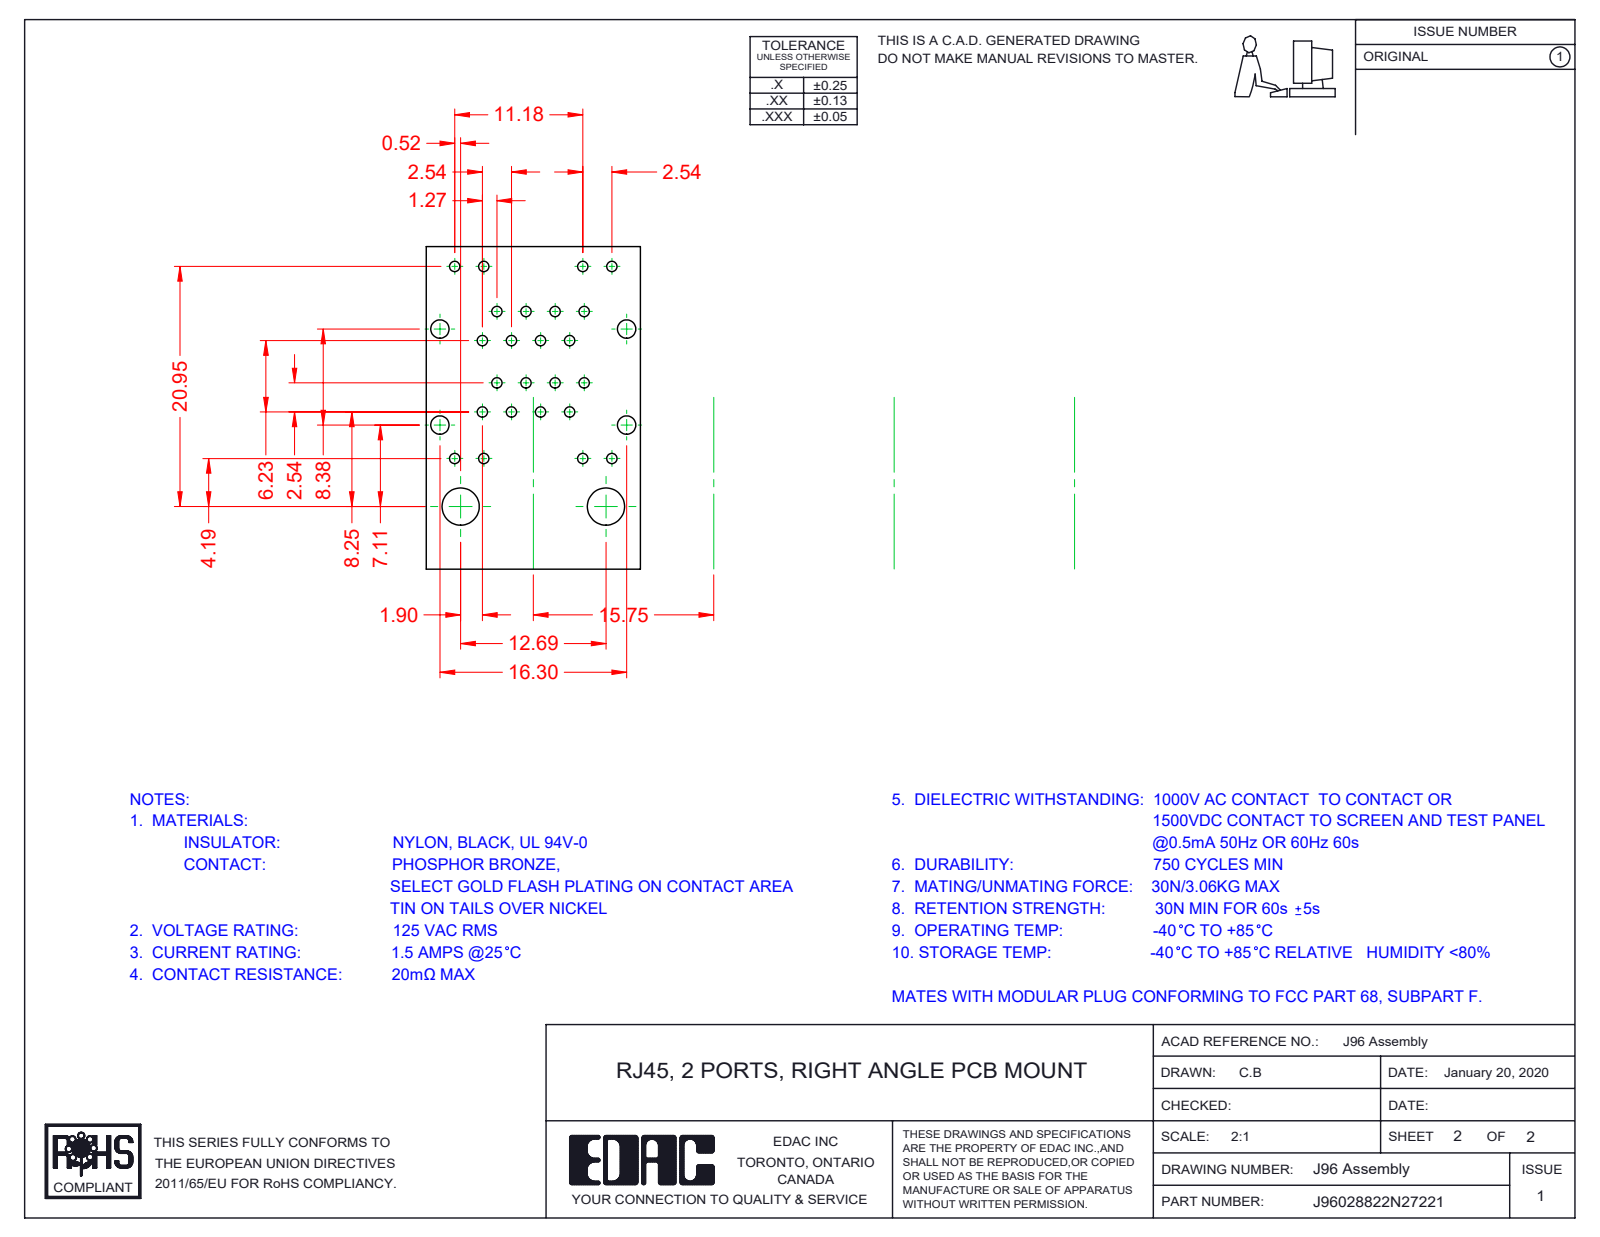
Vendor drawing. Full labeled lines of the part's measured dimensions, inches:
Part name (STEP PRODUCT): 96 LED LH Upper_2-Red; 96 Insulator Insert; 96 LED RH Upper_7-Green-Orange; 96 Contact Lock Upper (+8 more)
STEP written by: SolidWorks 2016 (CONFIG_CONTROL_DESIGN)
Units: inches
Bodies: 27 solids, 2421 faces (1865 planar, 450 cylindrical, 106 other)
Overall size (bounding box): 1.235 × 1.129 × 0.661
Volume: 0.418 in³ · Surface area: 29.6 in²
Partial cylindrical surfaces — rounded edges, fillets, slot ends (radius × count): R0.01 ×48, R0.006 ×32, R0.014 ×24, R0.02 ×16, R0.039 ×16, R0.008 ×14, R0.028 ×9, R0.079 ×5
Main face-to-face distances: 0.642, 0.634, 0.069, 0.65, 0.581, 0.061, 0.573, 0.021, 0.058, 0.441
